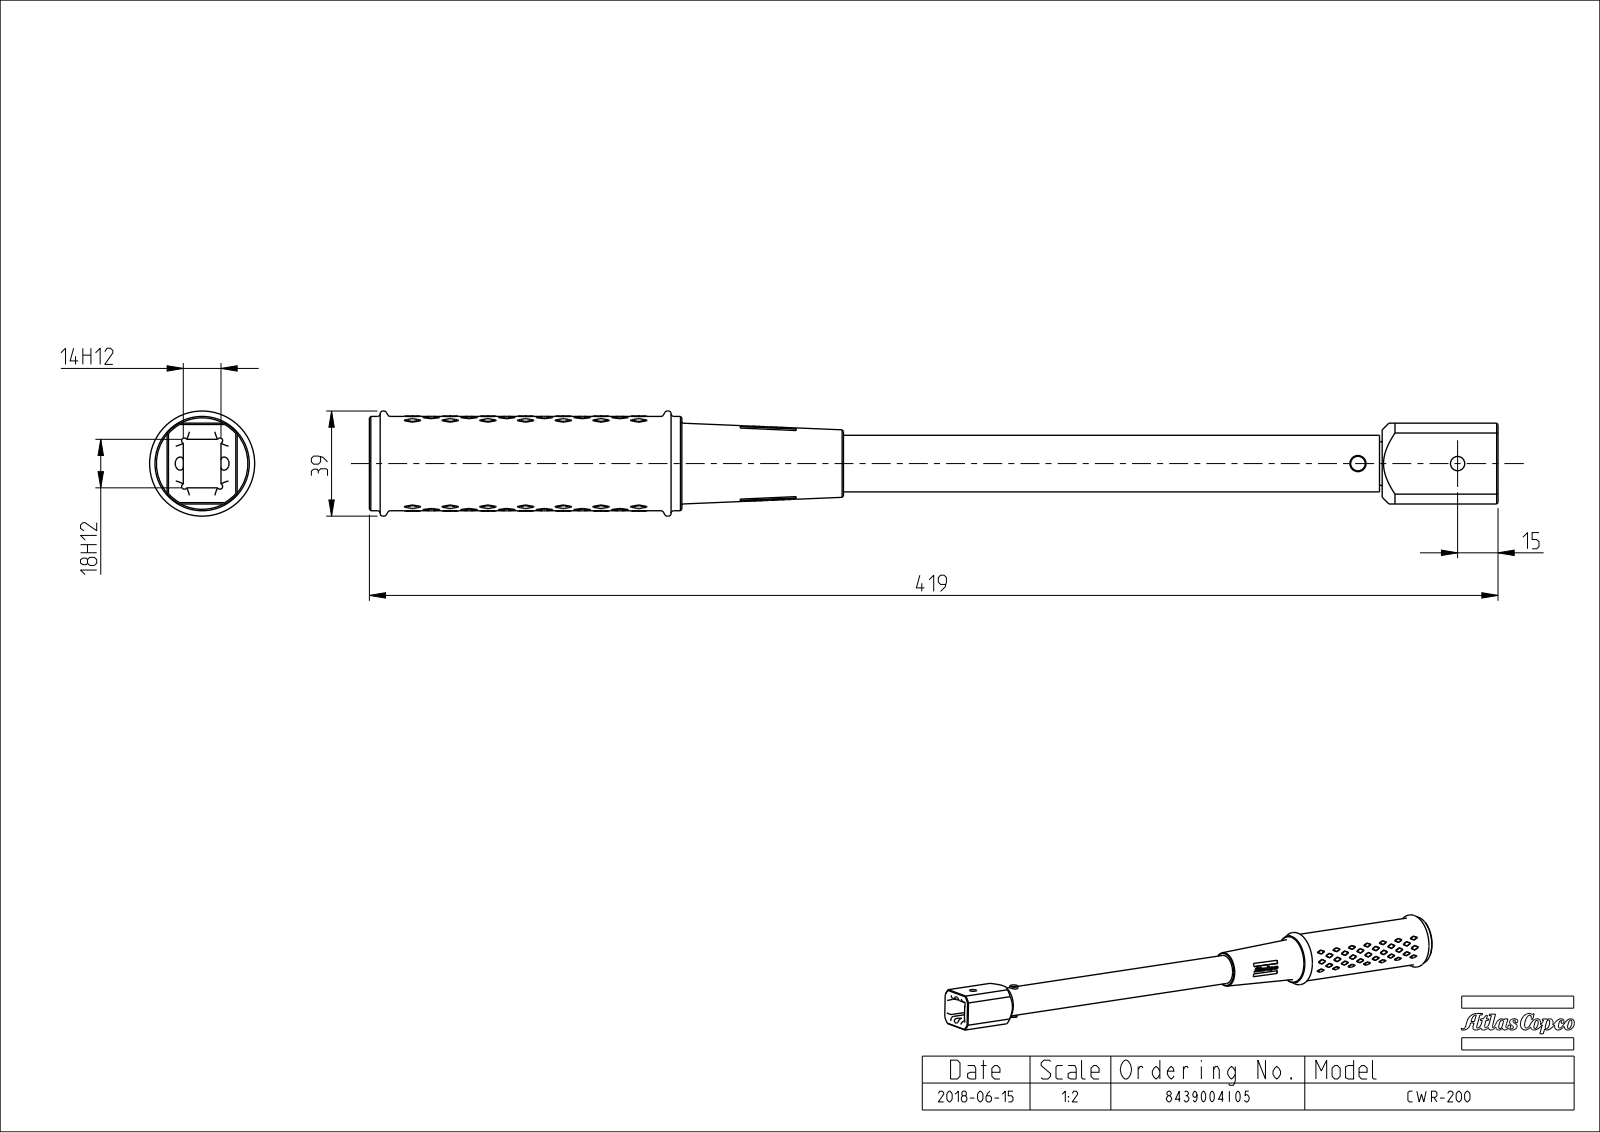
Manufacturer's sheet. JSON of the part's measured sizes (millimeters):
{"part_name": "8439004105", "step_written_by": "SolidWorks 2016 (AUTOMOTIVE_DESIGN)", "units": "millimeters", "bodies": {"solids": 0, "faces": 518, "planar": 36, "cylindrical": 39, "other": 443}, "overall_size": [419, 39, 39], "round_holes": [[5.3, 1], [16.5, 1]], "round_bosses_or_shafts": [[39, 1], [35, 1], [21, 1], [6, 1]], "partial_cylinders_radius": [[1, 4], [2.8, 4], [3, 2], [17.25, 1]], "face_to_face_distances": [6, 26, 30, 20, 24, 14, 376, 18, 43, 419]}
